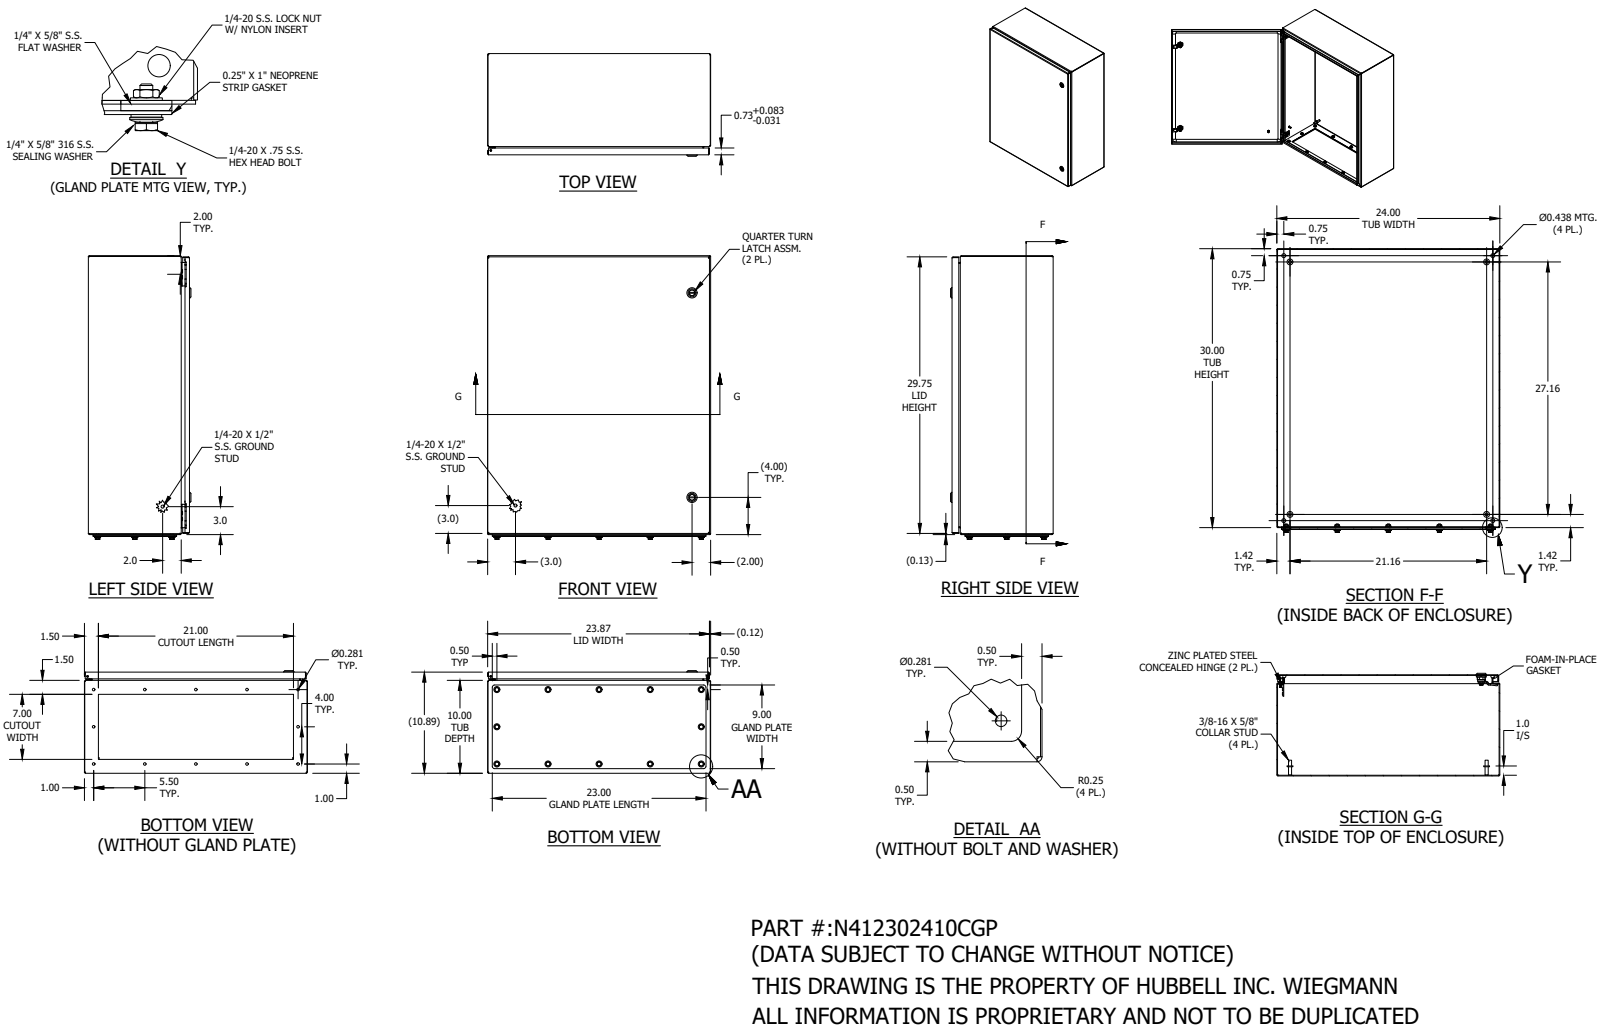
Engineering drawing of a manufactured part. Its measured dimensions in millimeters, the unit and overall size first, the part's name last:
Units: millimetres
Overall size (bounding box): 775.2 × 609.6 × 280.5
Round holes (diameter × count): ⌀7.1 ×14, ⌀5.4 ×12, ⌀7.4 ×12, ⌀7 ×9, ⌀4.1 ×8, ⌀6 ×6, ⌀6 ×6, ⌀8.9 ×6, ⌀4.8 ×5, ⌀2.4 ×4, ⌀4.2 ×4, ⌀11.1 ×4
Round bosses / shafts (diameter × count): ⌀6.4 ×22, ⌀15.9 ×14, ⌀16.5 ×12, ⌀15.2 ×12, ⌀11.1 ×12, ⌀9.1 ×4, ⌀8.4 ×4, ⌀8.1 ×4
Partial cylindrical surfaces — rounded edges, fillets, slot ends (radius × count): R0.3 ×56, R1.3 ×26, R0.5 ×21, R1.2 ×20, R3.1 ×20, R4 ×9, R3.2 ×8, R3.3 ×8
Main face-to-face distances: 1.9, 274.6, 272.7, 276.5, 765.3, 1.9, 607.7, 605.8, 609.6, 607.7
Hole centre spacings: 101.6, 139.7, 203.2, 279.4, 558.8, 568, 172.7, 419.1
Volume: 3 905 000 mm³ · Surface area: 3 862 000 mm²
Bodies: 95 solids, 2687 faces (1101 planar, 810 cylindrical, 776 other)
Part name (STEP PRODUCT): N412302410CGP
STEP written by: SolidWorks 2019 (AUTOMOTIVE_DESIGN)
